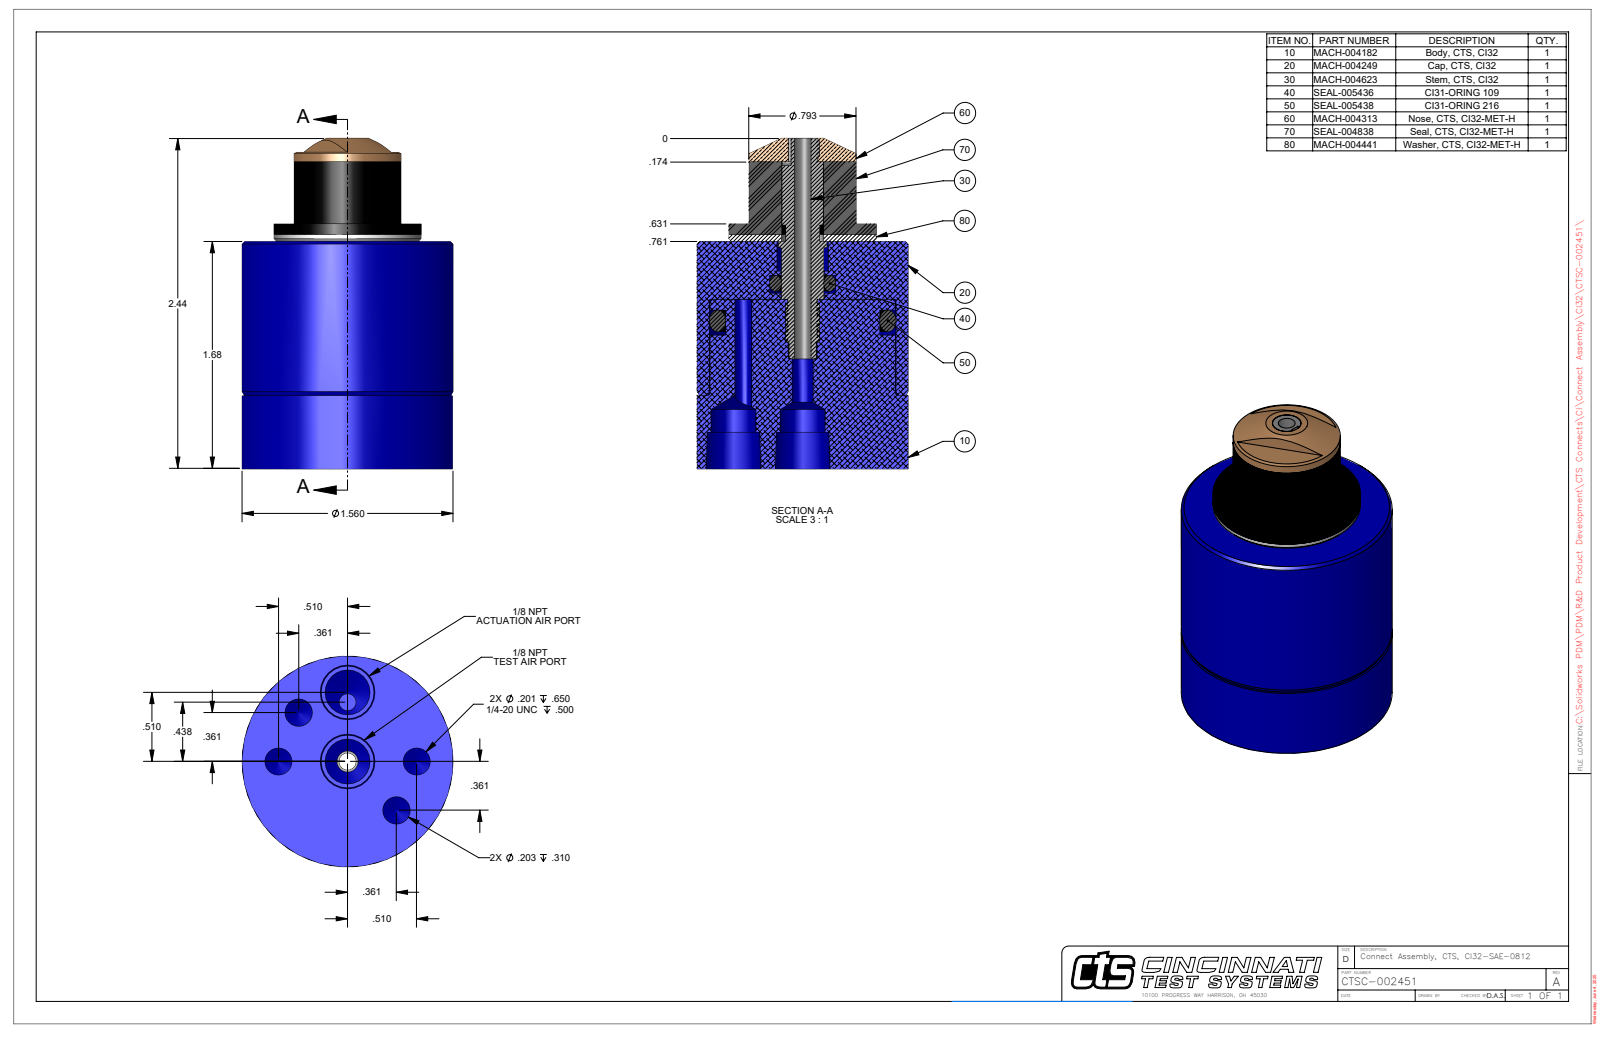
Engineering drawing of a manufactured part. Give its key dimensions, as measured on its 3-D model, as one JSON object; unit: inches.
{"part_name": "CTSC-002451", "step_written_by": "SolidWorks 2023 (AUTOMOTIVE_DESIGN)", "units": "inches", "bodies": {"solids": 1, "faces": 103, "planar": 29, "cylindrical": 40, "other": 34}, "overall_size": [2.438, 1.56, 1.56], "volume_in3": 3.398, "surface_area_in2": 19.78, "round_holes": [[0.125, 2], [0.201, 2], [0.203, 2], [0.332, 2], [0.156, 1], [0.213, 1], [0.314, 1], [0.38, 1], [1.377, 1]], "round_bosses_or_shafts": [[1.56, 1], [1.365, 1], [1.09, 1], [0.793, 1], [0.357, 1], [0.31, 1]], "face_to_face_distances": [1.677, 1.807, 0.13, 2.334, 0.657, 0.527, 0.542, 1.135, 1.265, 1.792], "hole_center_spacings": [0.51, 0.39, 0.942, 0.672, 0.721, 0.072, 0.369, 0.437]}
